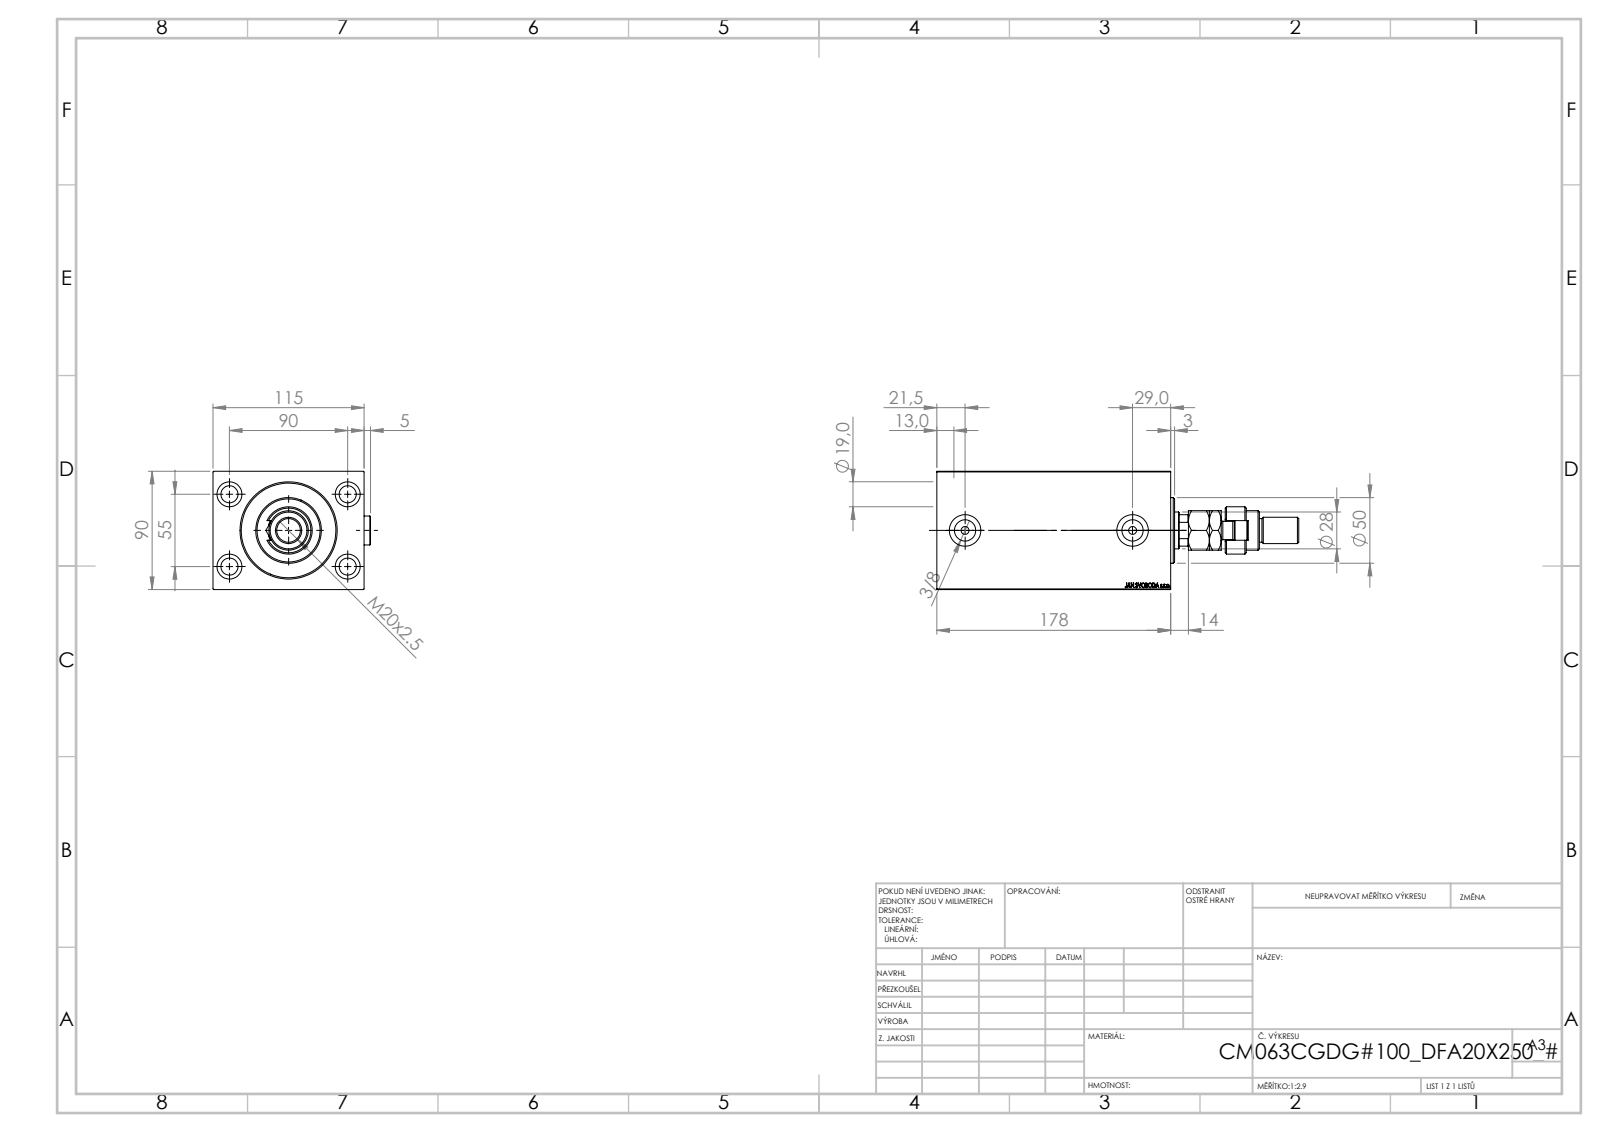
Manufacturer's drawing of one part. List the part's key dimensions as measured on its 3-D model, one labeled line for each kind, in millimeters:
Part name (STEP PRODUCT): V450CM_C_VCP; FEMALE_PART_FOR_DFA; V450CM_C_Body; V450CM_VC_B (+2 more)
STEP written by: SolidWorks 2019 (CONFIG_CONTROL_DESIGN)
Units: millimetres
Bodies: 7 solids, 1004 faces (471 planar, 91 cylindrical, 442 other)
Overall size (bounding box): 275.5 × 119.9 × 90
Volume: 1 526 000 mm³ · Surface area: 214 159 mm²
Round holes (diameter × count): ⌀13 ×4, ⌀19 ×4, ⌀6 ×2, ⌀16.17 ×2, ⌀24 ×2, ⌀18.5 ×1, ⌀28 ×1, ⌀31.5 ×1, ⌀63 ×1, ⌀65 ×1, ⌀72 ×1
Round bosses / shafts (diameter × count): ⌀22 ×3, ⌀50 ×1, ⌀36 ×1, ⌀30 ×1, ⌀20 ×1, ⌀18 ×1, ⌀14 ×1
Partial cylindrical surfaces — rounded edges, fillets, slot ends (radius × count): R7.5 ×1, R12 ×1, R13.5 ×1
Main face-to-face distances: 90, 115, 178, 17.5, 160.5, 13.5, 147, 164.5, 64.5, 47
Hole centre spacings: 52.74, 55, 90, 105.48, 127.5
